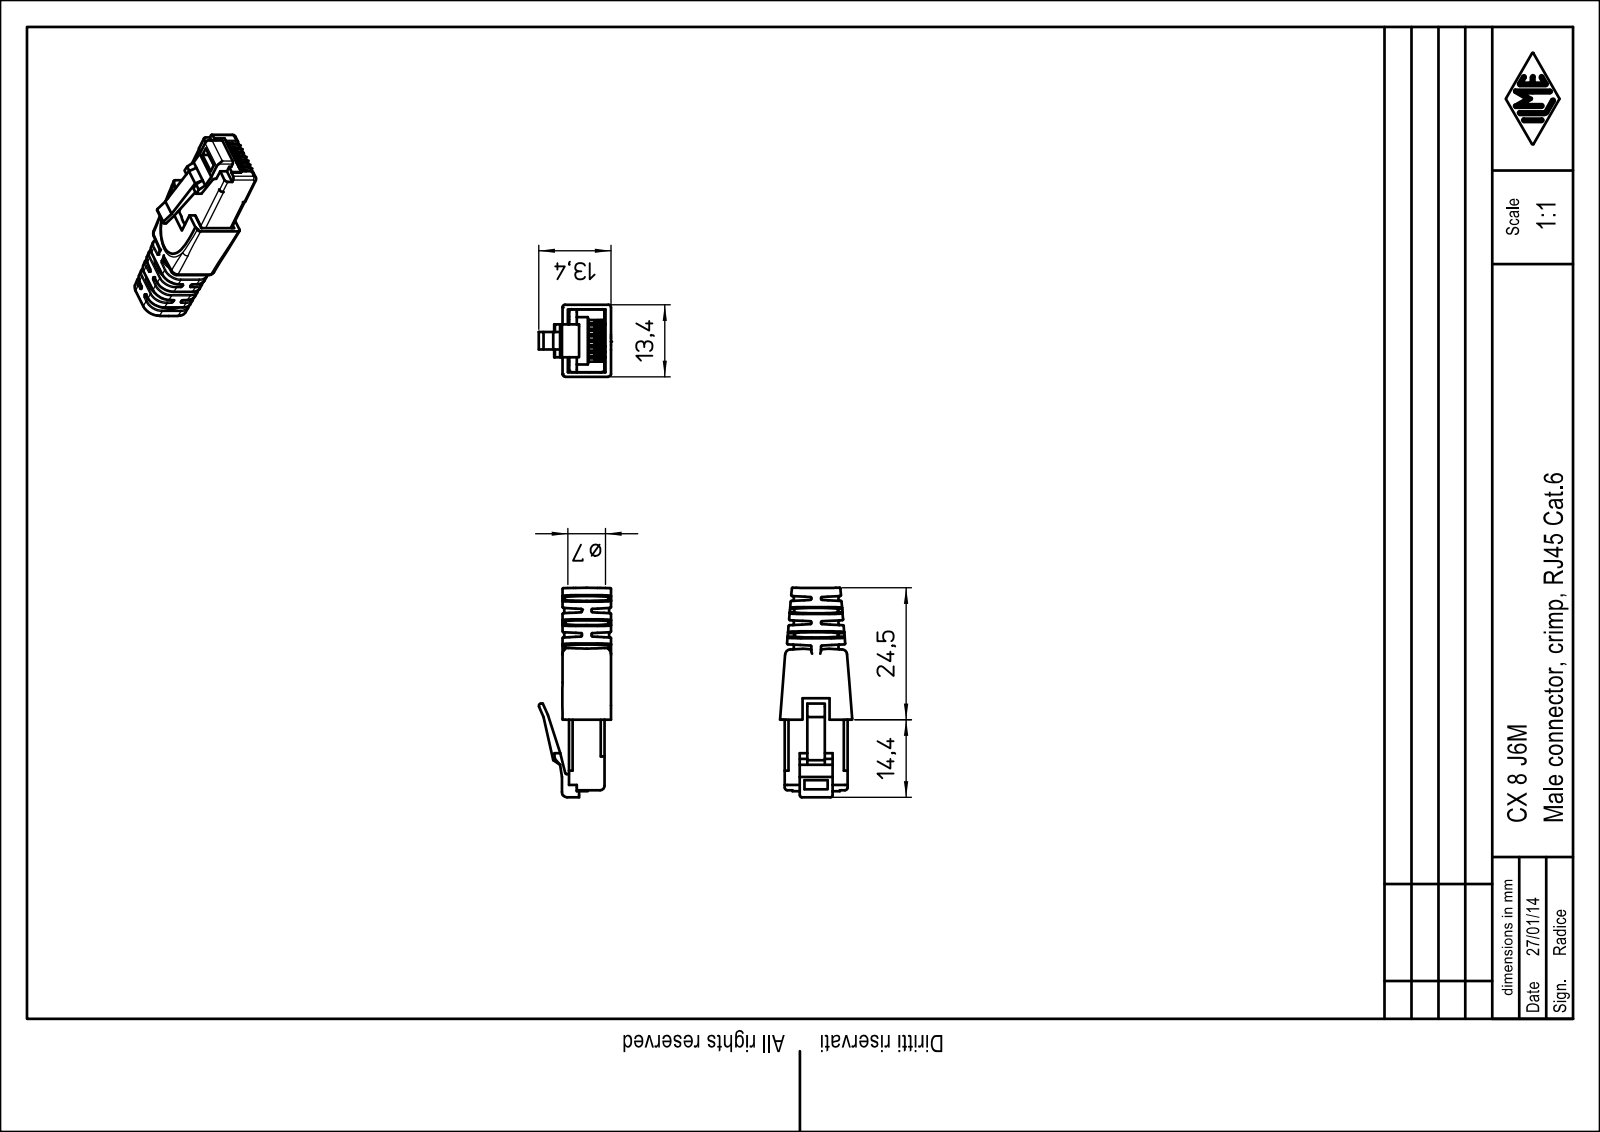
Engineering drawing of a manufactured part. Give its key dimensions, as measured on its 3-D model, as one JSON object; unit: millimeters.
{"part_name": "CX_8_J6M", "step_written_by": "Creo Elements/Direct Modeling 18.0B 02-Dec-2011 (C) Parametric Technology GmbH (AUTOMOTIVE_DESIGN)", "units": "millimeters", "bodies": {"solids": 1, "faces": 498, "planar": 185, "cylindrical": 209, "other": 104}, "overall_size": [38.25, 13.61, 13.2], "volume_mm3": 2522, "surface_area_mm2": 2832, "round_holes": [[6, 1]], "partial_cylinders_radius": [[0.5, 80], [0.28, 8], [0.2, 7], [1, 5], [0.8, 2], [0.38, 1], [2.62, 1]], "face_to_face_distances": [7.65, 1.05, 1, 1.11, 1.55, 2.22, 2, 3.33, 8.7, 5.55]}
